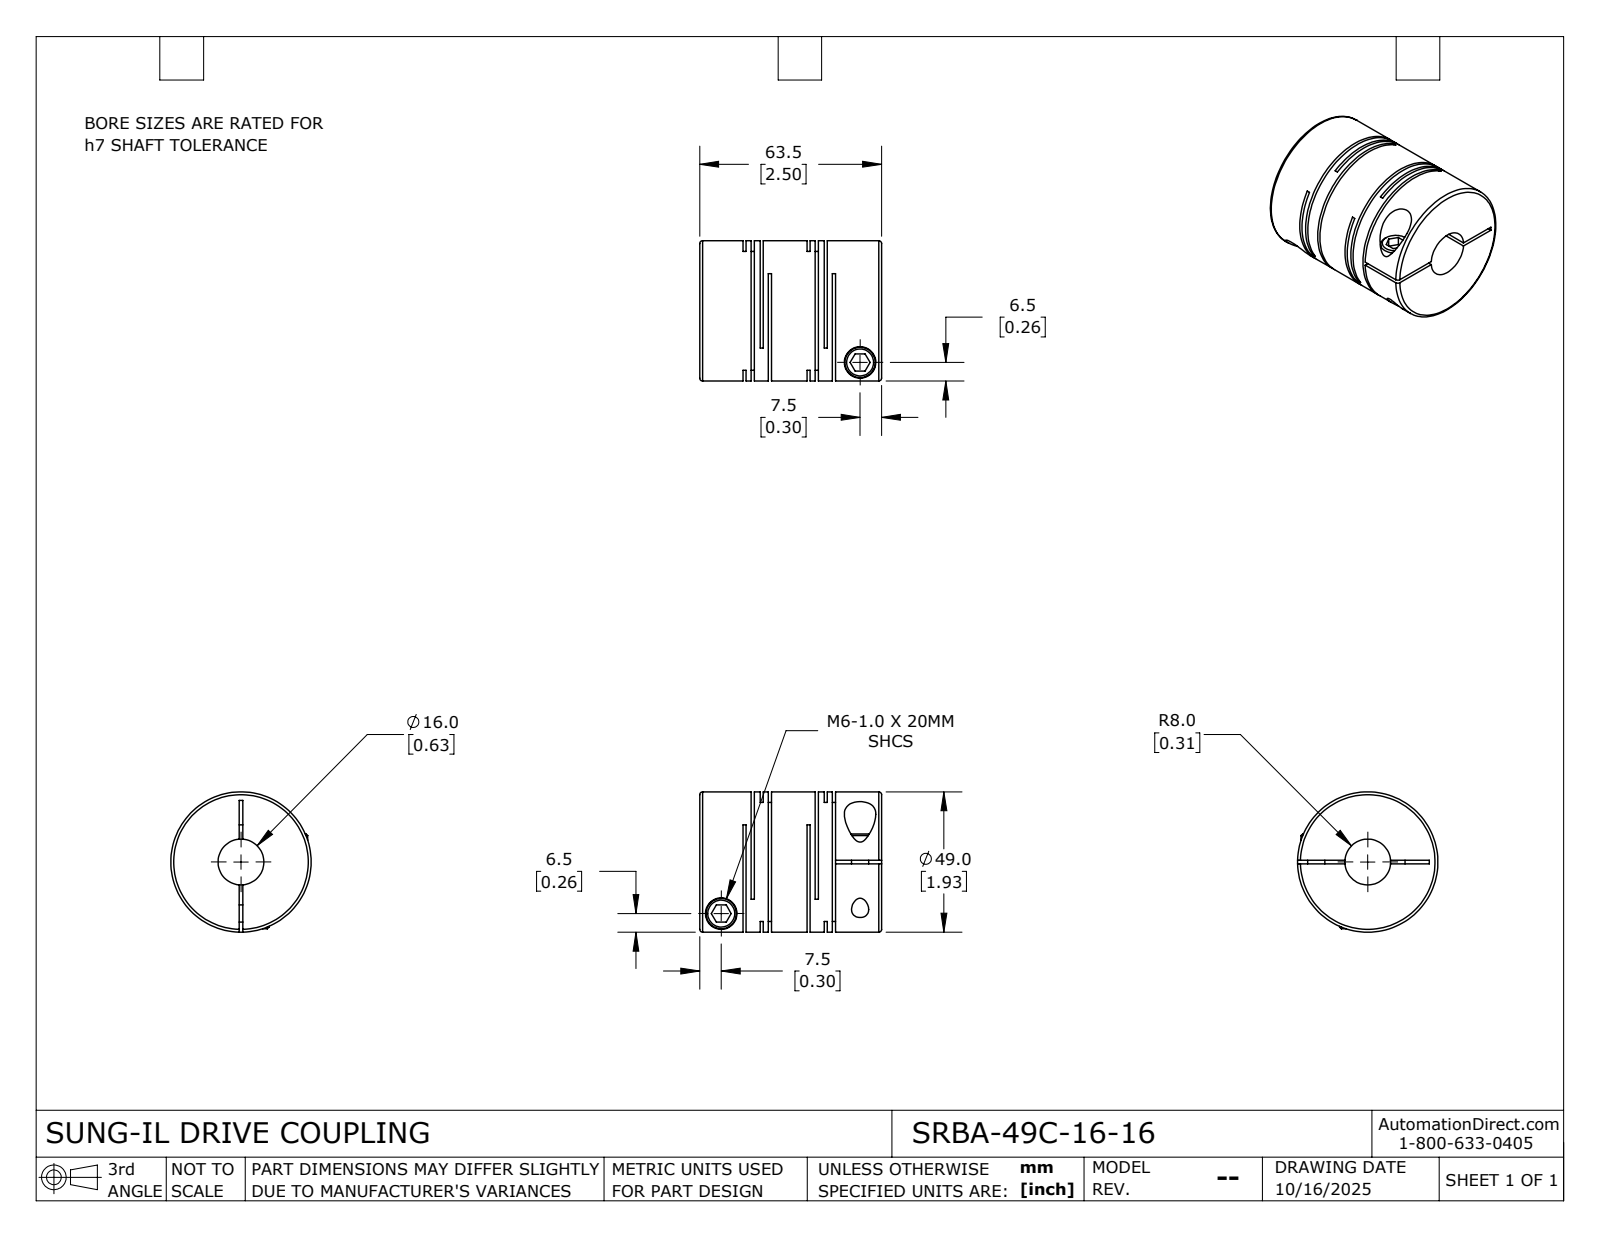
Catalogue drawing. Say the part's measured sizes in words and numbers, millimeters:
The part is named "SRBA-49C-16-16". Its 3-D file was written by "SolidWorks 2024 (CONFIG_CONTROL_DESIGN)". It is 1 solid with 115 faces: 60 planar, 42 cylindrical and 13 other. Overall it measures 63.5 by 49 by 49 millimeters. Its volume is 92 233 cubic millimeters and its surface area 39 553 square millimeters. Round holes: 2 of diameter 6, 2 of diameter 11, 1 of diameter 16. Round bosses or shafts: 2 of diameter 10.6, 1 of diameter 49. The main face-to-face distances are 6, 1.1, 22.35, 2.85, 21.25, 3.15, 1.75, 4.9, 19.5, 16.35.
